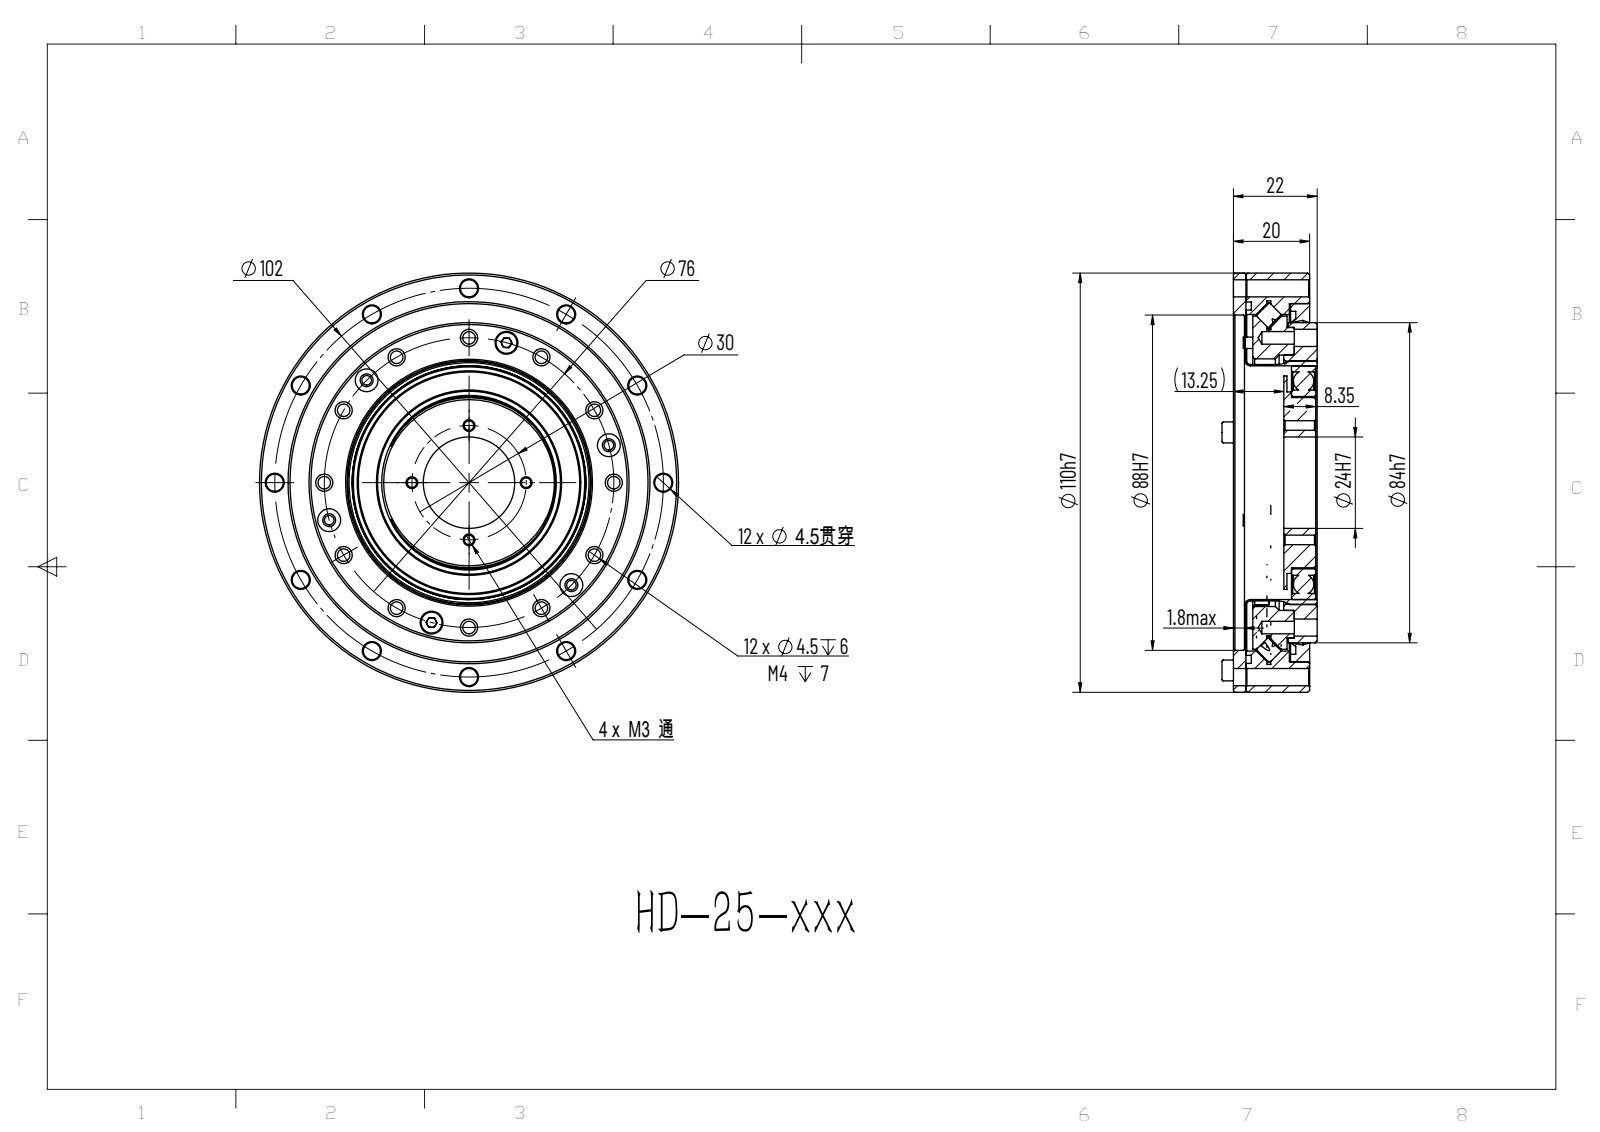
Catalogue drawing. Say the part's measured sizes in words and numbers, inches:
The part is named "HD-25-xxx; hexagon socket head cap screws gb_GB_FASTENER_SCREWS_HSHCS M3X16-N; HD-25-????_?? <1>; HD-25-?? (+3 more)". Its 3-D file was written by "ONSHAPE BY PTC INC, 1.201 (AP242_MANAGED_MODEL_BASED_3D_ENGINEERING_MIM_LF)". It is 19 solids with 504 faces: 217 planar, 137 cylindrical and 150 other. Overall it measures 4.331 by 4.331 by 0.984 inches. Its volume is 7.293 cubic inches and its surface area 135.1 square inches. Round holes: 24 of diameter 0.177, 18 of diameter 0.098, 12 of diameter 0.13, 6 of diameter 0.134, 6 of diameter 0.236, 4 of diameter 0.138, 1 of diameter 0.945, 1 of diameter 1.78, 1 of diameter 2.288, 1 of diameter 2.415, 1 of diameter 2.512, 1 of diameter 2.559. Round bosses or shafts: 12 of diameter 0.217, 12 of diameter 0.118, 1 of diameter 4.331, 1 of diameter 3.567, 1 of diameter 3.441, 1 of diameter 3.307, 1 of diameter 3.163, 1 of diameter 2.519. The main face-to-face distances are 0.5, 0.657, 0.157, 0.63, 0.13, 0.787, 0.201, 0.071, 0.115, 0.015. The hole center spacings are 2.008, 1.807, 2.504, 3.045, 1.496, 1.039, 3.387, 1.033.
